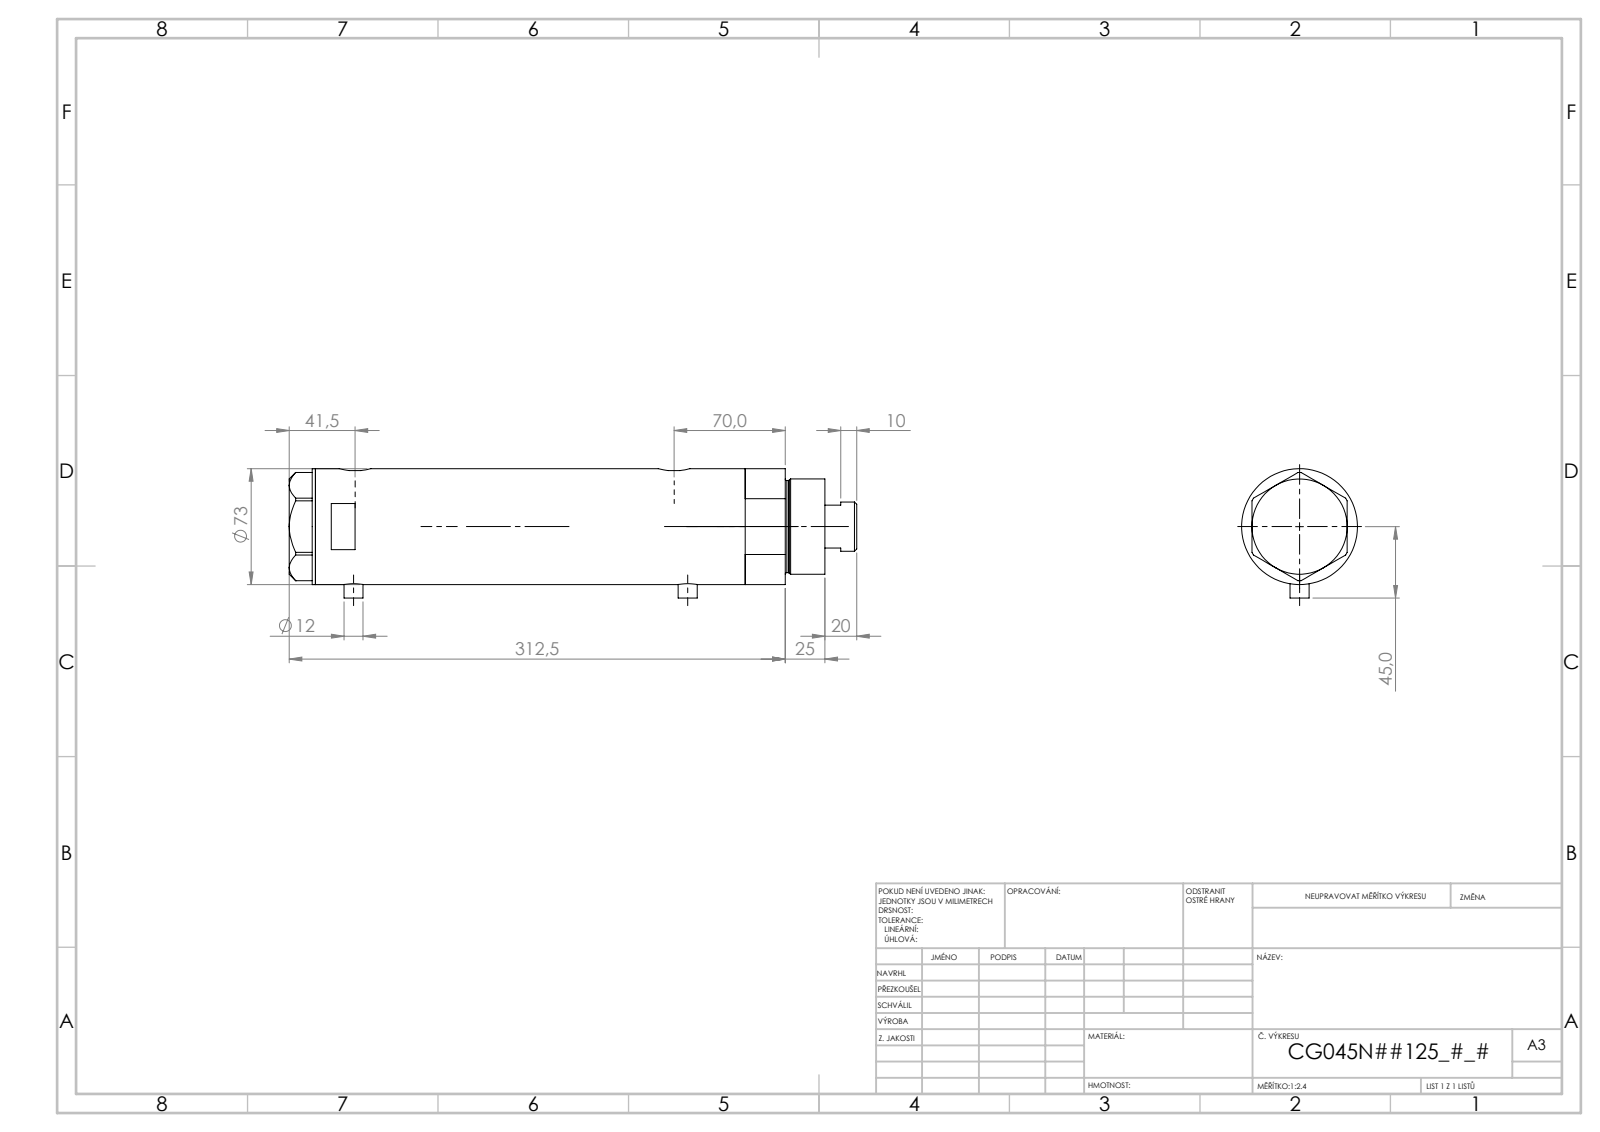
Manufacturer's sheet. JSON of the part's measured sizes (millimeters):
{"part_name": "V270CG_VC; V270CG_FRONT; V270CG_MIDDLE; V270CG_BACK", "step_written_by": "SolidWorks 2019 (CONFIG_CONTROL_DESIGN)", "units": "millimeters", "bodies": {"solids": 4, "faces": 125, "planar": 50, "cylindrical": 55, "other": 20}, "overall_size": [316.52, 74.1, 73], "volume_mm3": 1092000, "surface_area_mm2": 178845, "round_holes": [[5, 2], [12.5, 2], [13.16, 2], [10.5, 1], [32, 1], [33.5, 1], [45, 1], [48, 1], [64, 1]], "round_bosses_or_shafts": [[12, 2], [73, 1], [60, 1], [58, 1], [31, 1]], "partial_cylinders_radius": [[10, 2]], "face_to_face_distances": [192.14, 16.5, 208.64, 280.01, 254.02, 42.5, 26, 166.14, 296.51, 254.01], "hole_center_spacings": [176.65, 0.99, 1, 8.5, 8.51, 167.15, 168.14, 168.15]}
